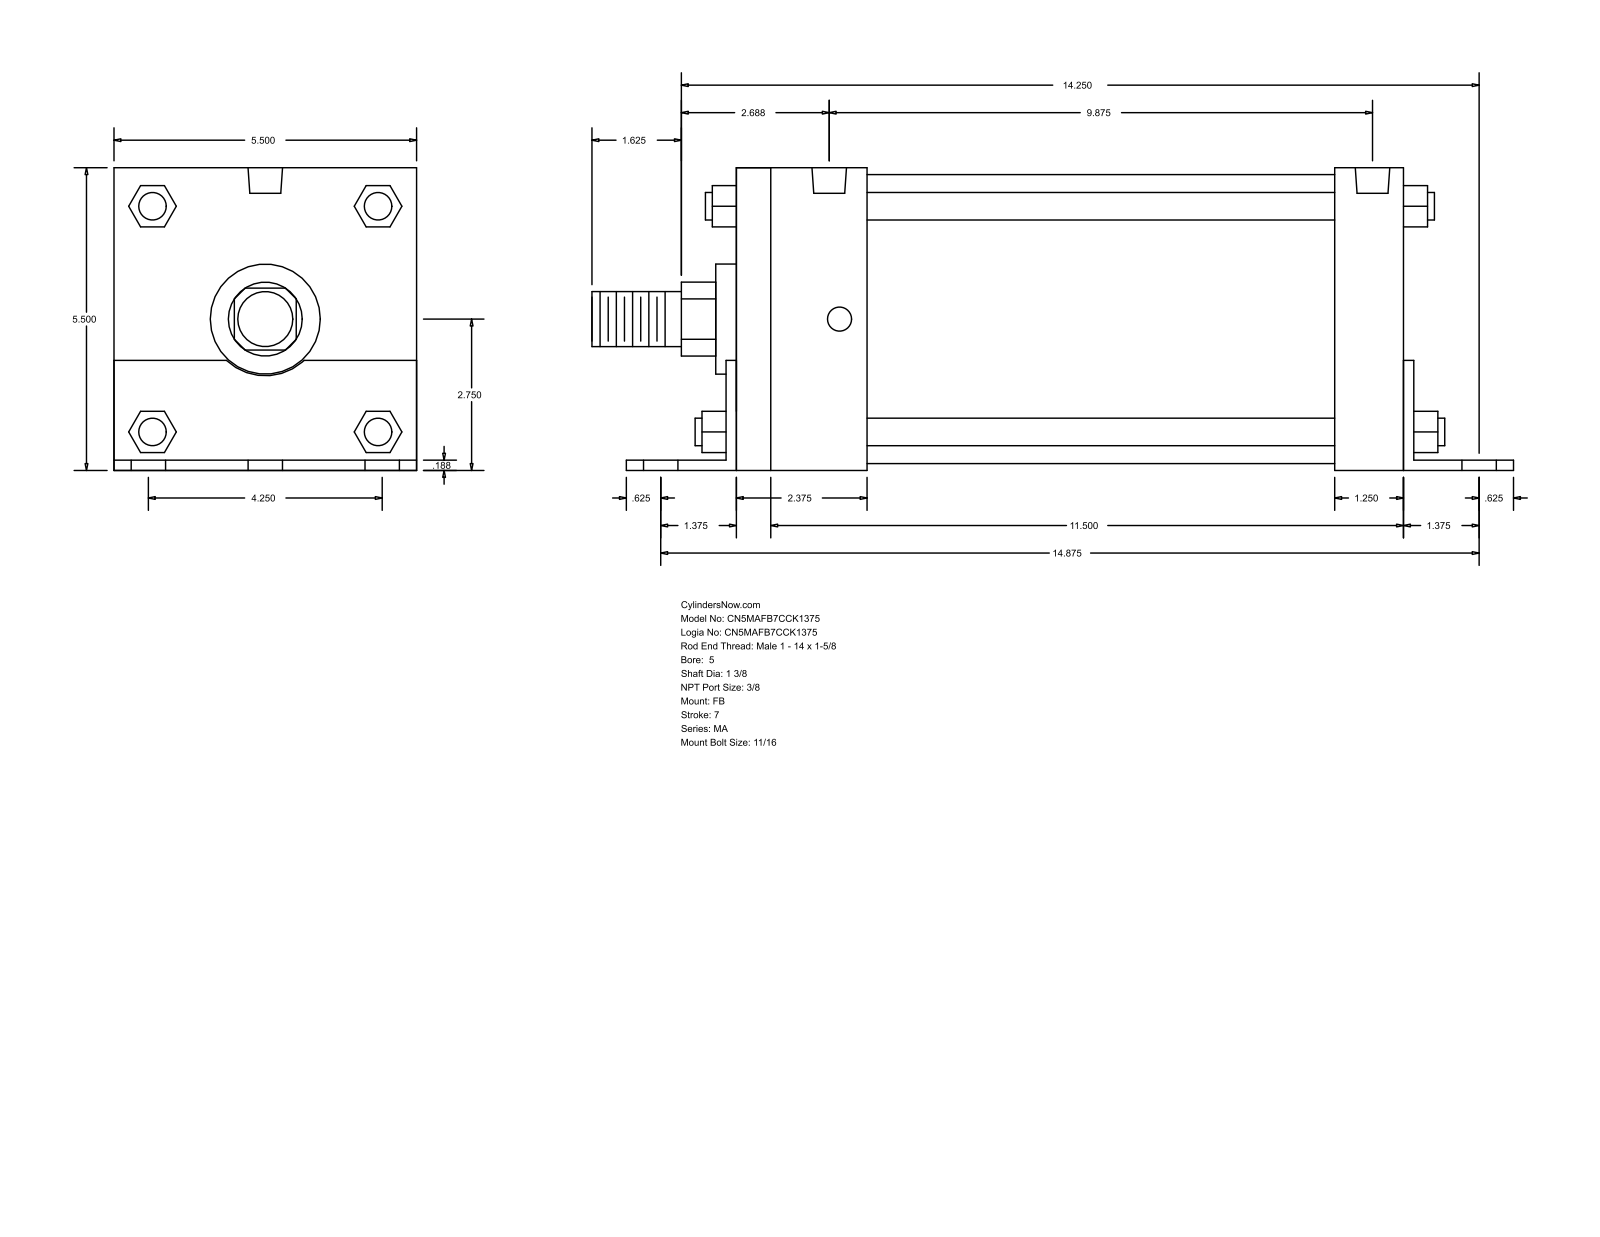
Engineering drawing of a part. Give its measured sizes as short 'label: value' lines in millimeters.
name: MA_FB__0500_1.375
written by: GSSL Pune (CONFIG_CONTROL_DESIGN)
unit: mm
bodies: 0 solids, 140 faces (105 planar, 35 cylindrical, 0 other)
size: 425.45 × 139.75 × 139.7
holes: 6× ⌀17.46, 4× ⌀11.11, 2× ⌀15.93
bosses: 4× ⌀12.7, 1× ⌀133.35, 1× ⌀50.8, 1× ⌀34.92, 1× ⌀25.4
rounds: 1× R17.06, 1× R26.16
face distances: 139.7, 4.76, 139.75, 312.74, 4.71, 134.99, 307.98, 317.5, 36.52, 65.08
hole spacings: 53.98, 381.67, 377.83, 4.77, 73.04, 76.34, 94.68, 98.64
